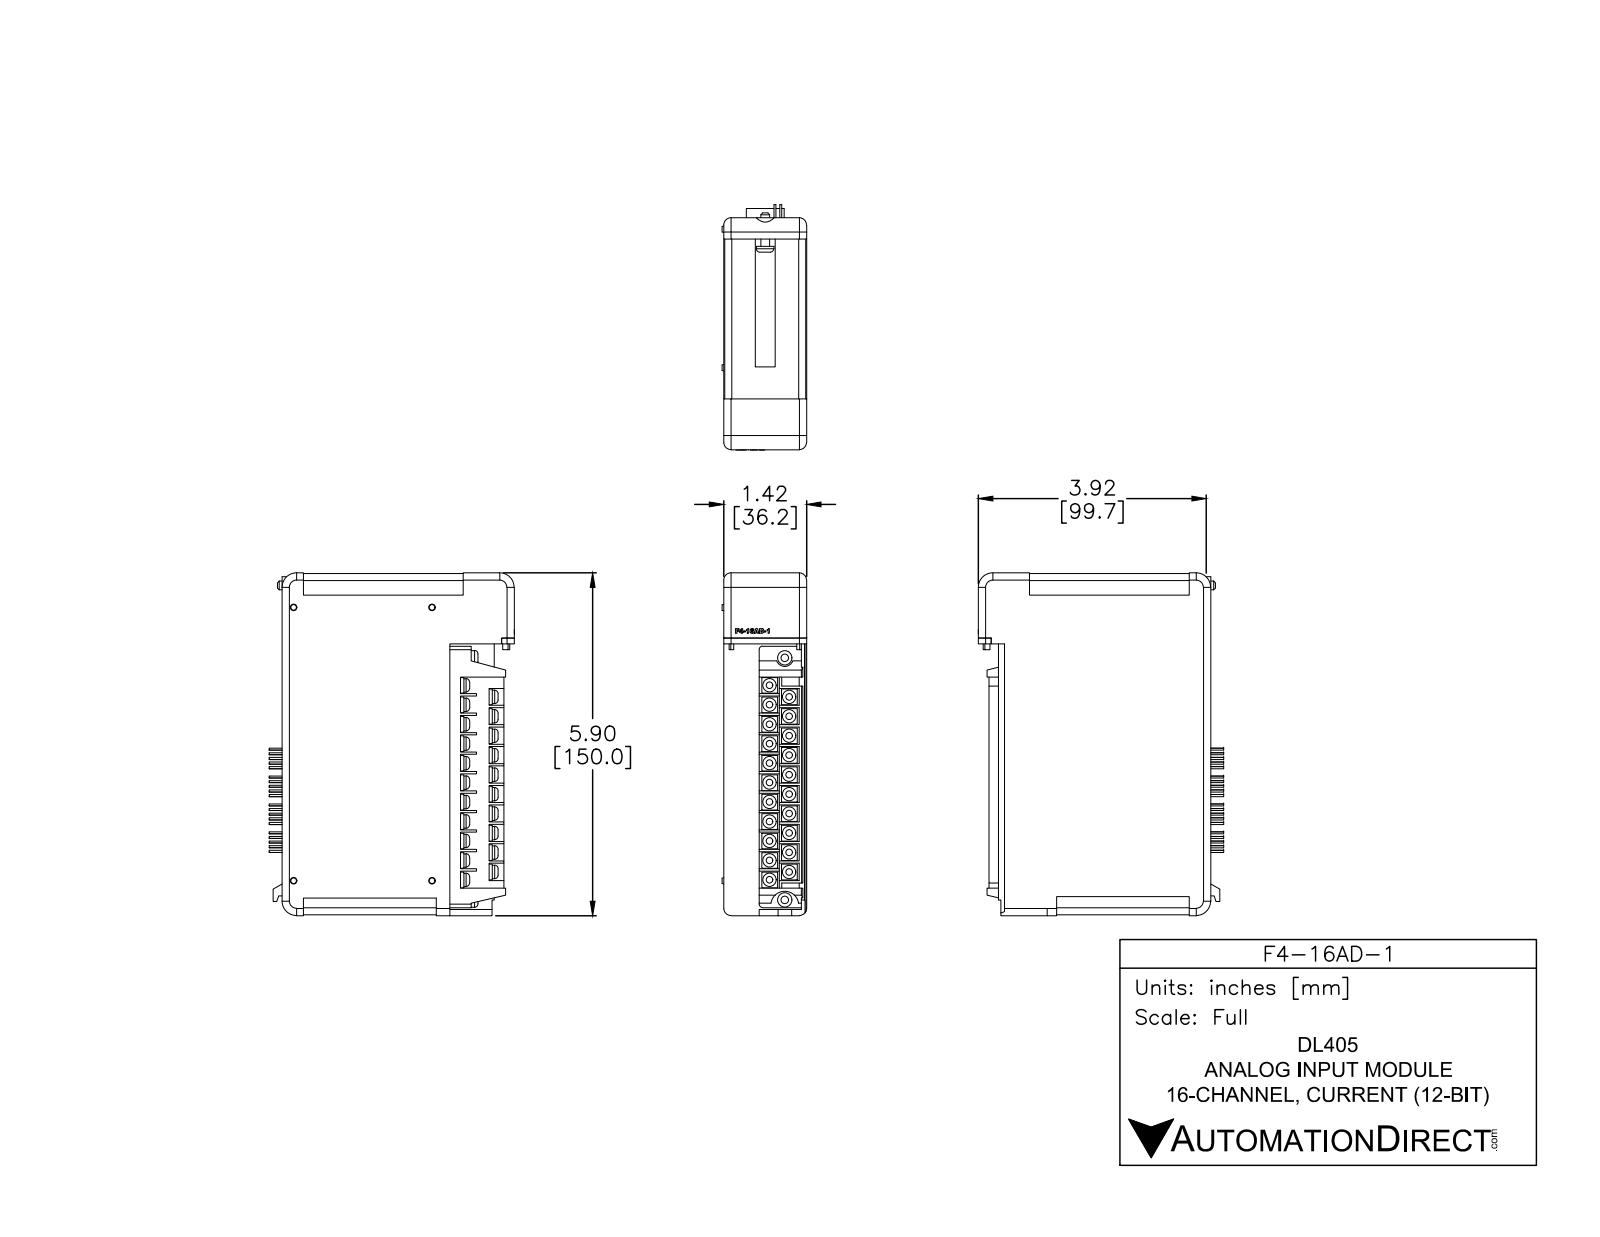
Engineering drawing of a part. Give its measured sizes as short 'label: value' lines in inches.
name: F4-16AD-1
written by: SolidWorks 2014 (AUTOMOTIVE_DESIGN)
unit: in
bodies: 6 solids, 891 faces (561 planar, 246 cylindrical, 84 other)
size: 5.905 × 4.223 × 1.455
volume: 27.6 in³; area: 90.48 in²
bosses: 21× ⌀0.23, 20× ⌀0.035, 20× ⌀0.035, 2× ⌀0.25, 1× ⌀0.3, 1× ⌀0.15
rounds: 82× R0.015, 8× R0.125, 4× R0.12, 3× R0.25, 2× R0.03, 2× R0.06, 1× R0.149, 1× R0.151
face distances: 1.425, 0.015, 2.89, 5.875, 1.41, 0.47, 0.955, 5.89, 1.21, 0.345
